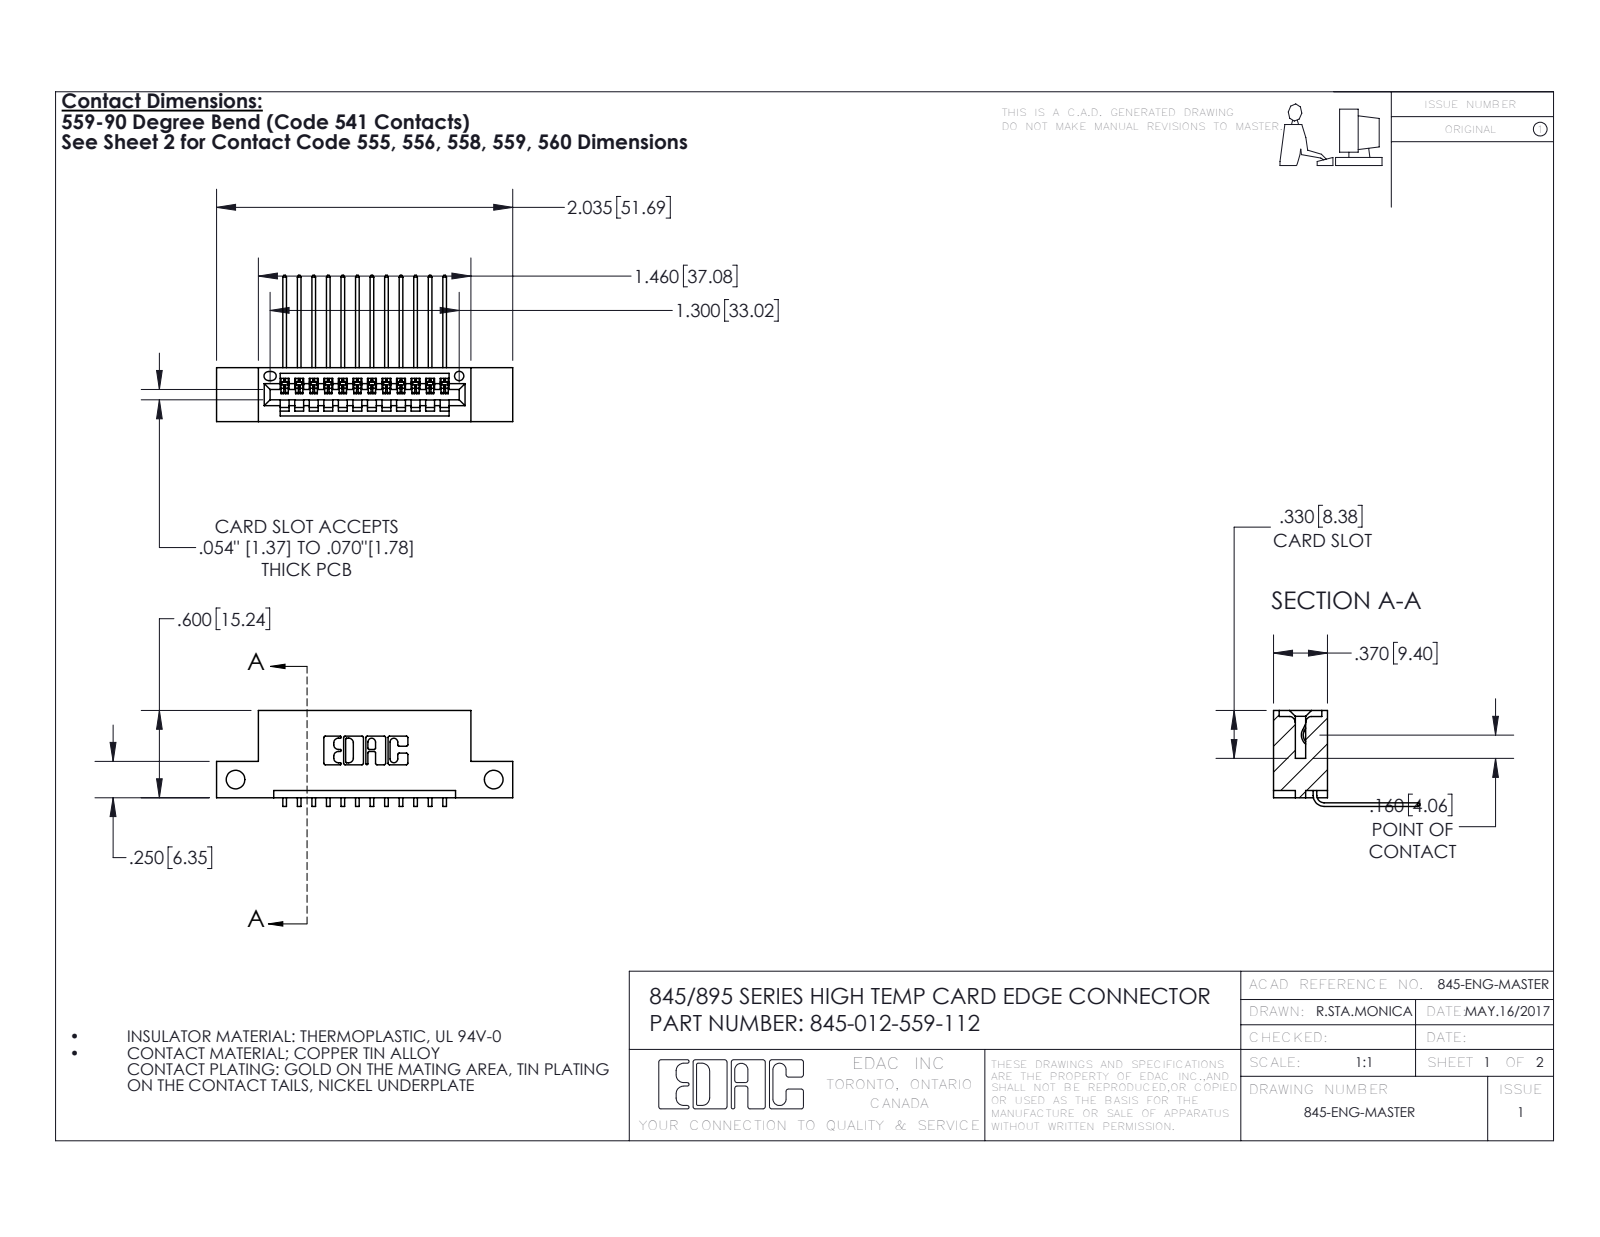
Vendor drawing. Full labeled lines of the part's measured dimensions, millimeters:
Part name (STEP PRODUCT): 345 Part_Flush Mounting Lugs - Side Mount; 345-292-001_558 559 Tail - 1; 345-012-559-112
STEP written by: SolidWorks 2016 (CONFIG_CONTROL_DESIGN)
Units: millimetres
Bodies: 13 solids, 846 faces (584 planar, 262 cylindrical, 0 other)
Overall size (bounding box): 51.7 × 25.5 × 16.7
Volume: 4 620 mm³ · Surface area: 5 820 mm²
Round holes (diameter × count): ⌀3.3 ×2, ⌀1.6 ×1
Partial cylindrical surfaces — rounded edges, fillets, slot ends (radius × count): R0.2 ×24, R0.3 ×22, R0.2 ×6, R0.8 ×6, R0.7 ×3, R0.8 ×2, R1 ×2, R0.4 ×1
Main face-to-face distances: 5.1, 7.6, 1.8, 9.4, 2.5, 6.9, 0.6, 2.5, 15.2, 7.6
Hole centre spacings: 45.1
